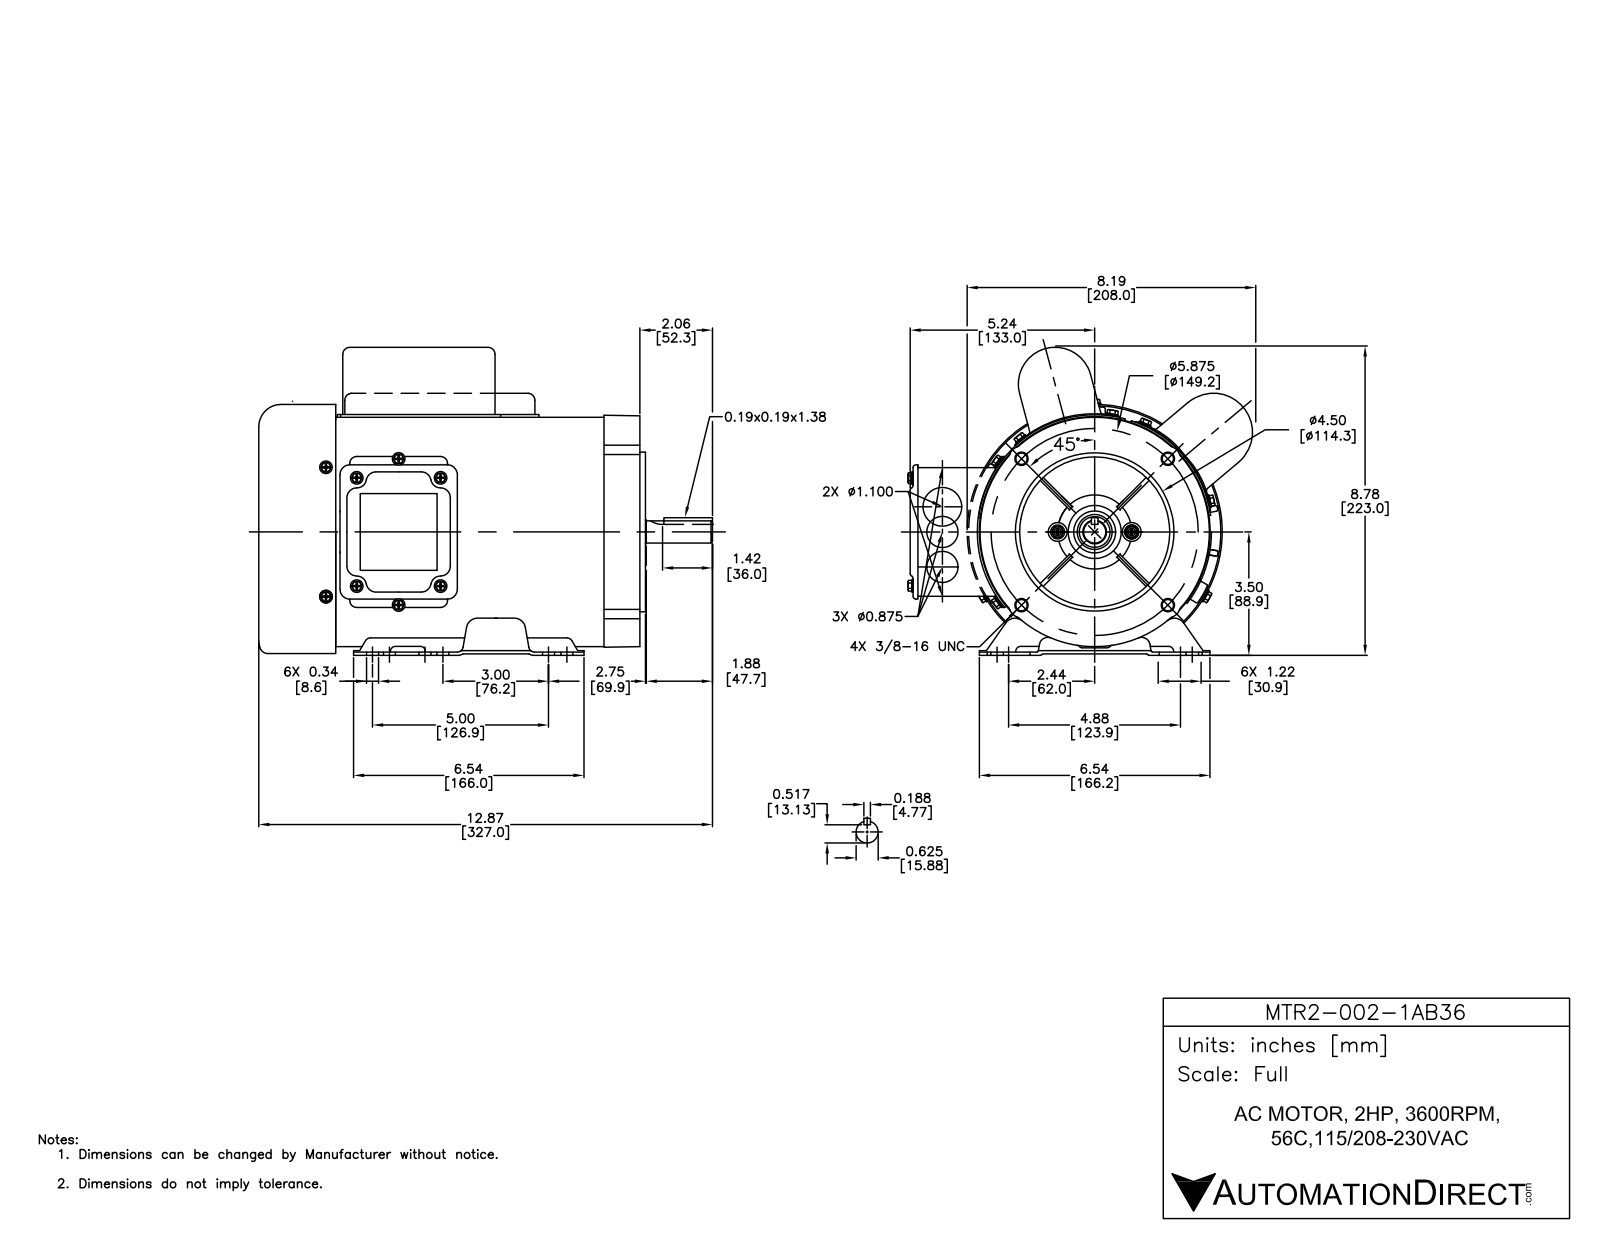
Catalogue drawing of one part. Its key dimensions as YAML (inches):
part_name: "Elec Cover bolt Hex Washer Screw_AI_IN-HWMS 0.164-32x0.3125x0.3125-N; Fan; Shaft Key1875 x 1875 x 1.38; Fan Guard A (+8 more)"
step_written_by: "SolidWorks 2015 (AUTOMOTIVE_DESIGN)"
units: inches
bodies: {solids: 58, faces: 2680, planar: 1024, cylindrical: 1049, other: 607}
overall_size: [12.872, 9.408, 8.966]
volume: 56.11
surface_area: 1327
round_holes:
  - {diameter: 0.219, count: 13}
  - {diameter: 0.197, count: 12}
  - {diameter: 0.136, count: 9}
  - {diameter: 0.276, count: 8}
  - {diameter: 0.248, count: 7}
  - {diameter: 0.217, count: 6}
  - {diameter: 0.344, count: 6}
  - {diameter: 0.154, count: 4}
  - {diameter: 0.313, count: 4}
  - {diameter: 0.709, count: 3}
  - {diameter: 0.134, count: 2}
  - {diameter: 0.273, count: 2}
round_bosses_or_shafts:
  - {diameter: 0.348, count: 13}
  - {diameter: 0.164, count: 13}
  - {diameter: 0.248, count: 7}
  - {diameter: 0.551, count: 2}
  - {diameter: 0.414, count: 2}
  - {diameter: 0.19, count: 2}
  - {diameter: 7.185, count: 1}
  - {diameter: 6.496, count: 1}
partial_cylinders:
  - {radius: 0.118, count: 101}
  - {radius: 0.039, count: 62}
  - {radius: 0.228, count: 32}
  - {radius: 0.075, count: 23}
  - {radius: 0.197, count: 22}
  - {radius: 0.315, count: 18}
  - {radius: 0.276, count: 17}
  - {radius: 0.1, count: 16}
face_to_face_distances: [0.039, 0.236, 0.118, 0.063, 9.679, 2.244, 0.075, 1.388, 1.624, 1.348]
hole_center_spacings: [3.031, 4.331, 4.221, 4.287, 0.185, 5.967, 5.969, 6.061]
